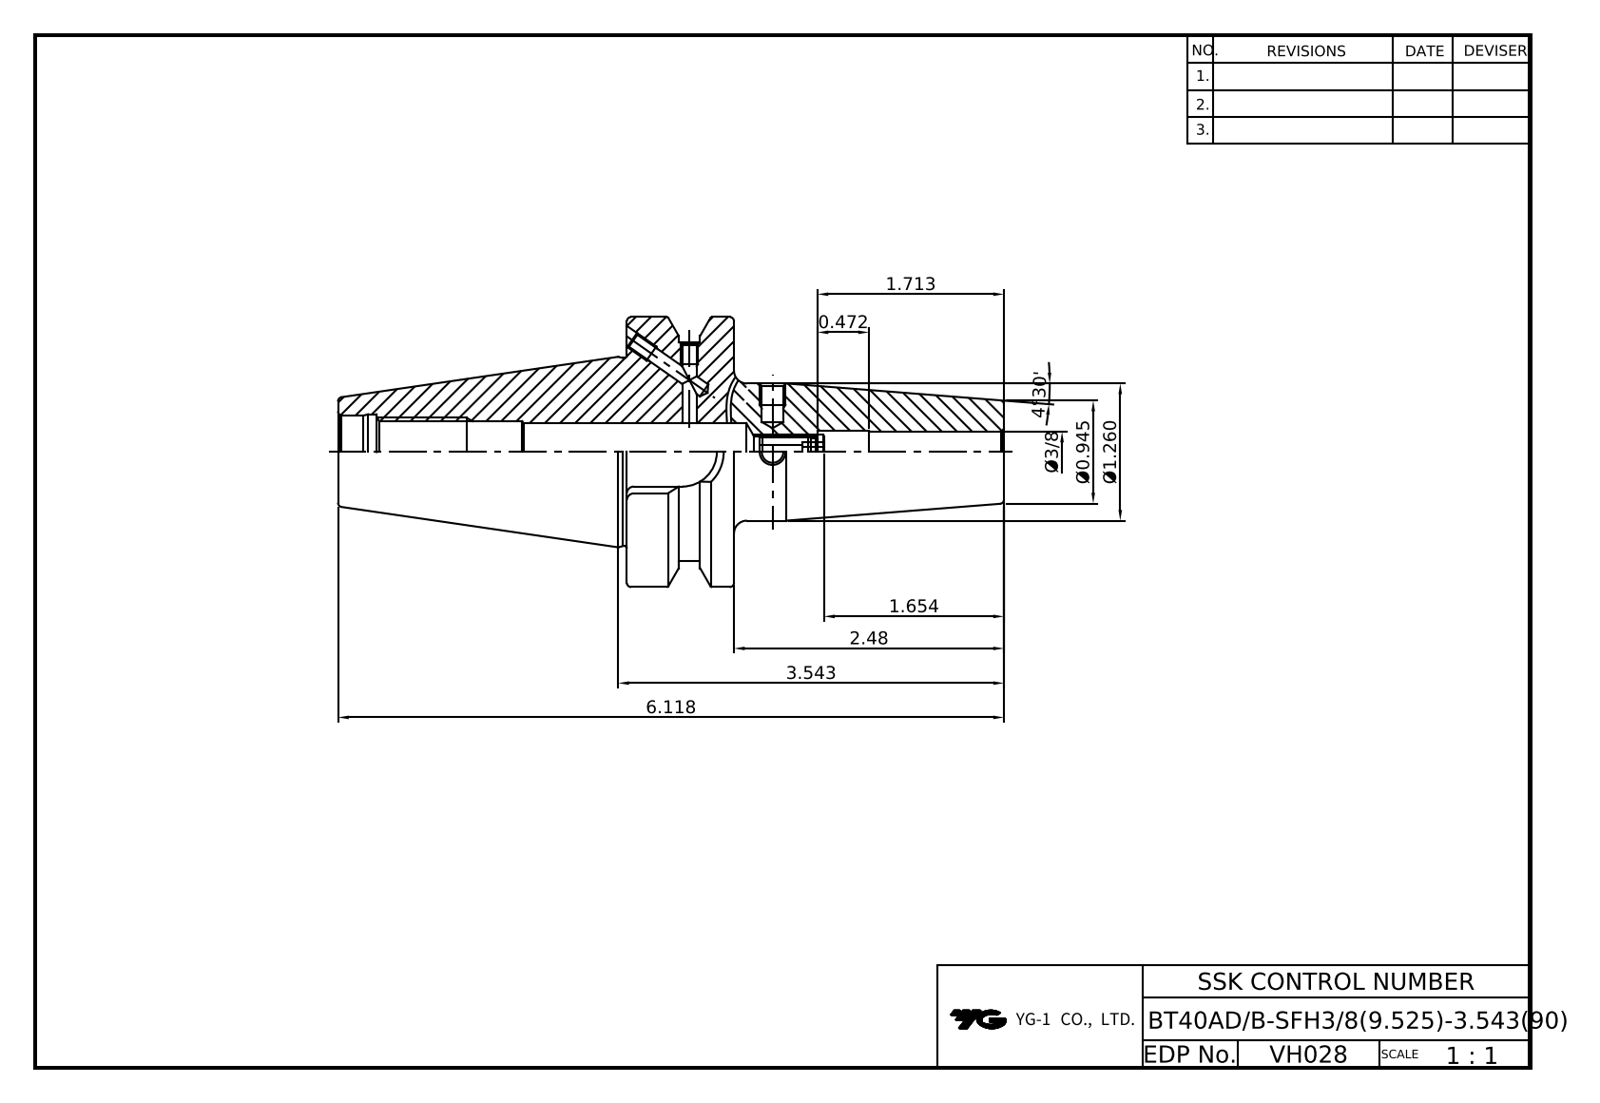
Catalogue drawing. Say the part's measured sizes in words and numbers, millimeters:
The part is named "BT40ADB-SFH6_35-90". Its 3-D file was written by "CREO PARAMETRIC BY PTC INC, 2018500 (CONFIG_CONTROL_DESIGN)". It is 1 solid with 92 faces: 22 planar, 30 cylindrical and 40 other. Overall it measures 155.4 by 63 by 63 millimeters. Its volume is 156 220 cubic millimeters and its surface area 31 298 square millimeters. Round holes: 1 of diameter 7, 1 of diameter 8, 1 of diameter 9.53, 1 of diameter 10.12, 1 of diameter 13.5, 1 of diameter 14, 1 of diameter 16, 1 of diameter 17, 1 of diameter 17.6. Round bosses or shafts: 1 of diameter 63, 1 of diameter 51, 1 of diameter 44, 1 of diameter 32. Partial cylindrical surfaces (rounded edges, fillets, slot ends): 1 of radius 8.05. The main face-to-face distances are 25, 45.2, 88, 63, 17.1, 7.9, 70.9, 12.1, 5, 12.9.
